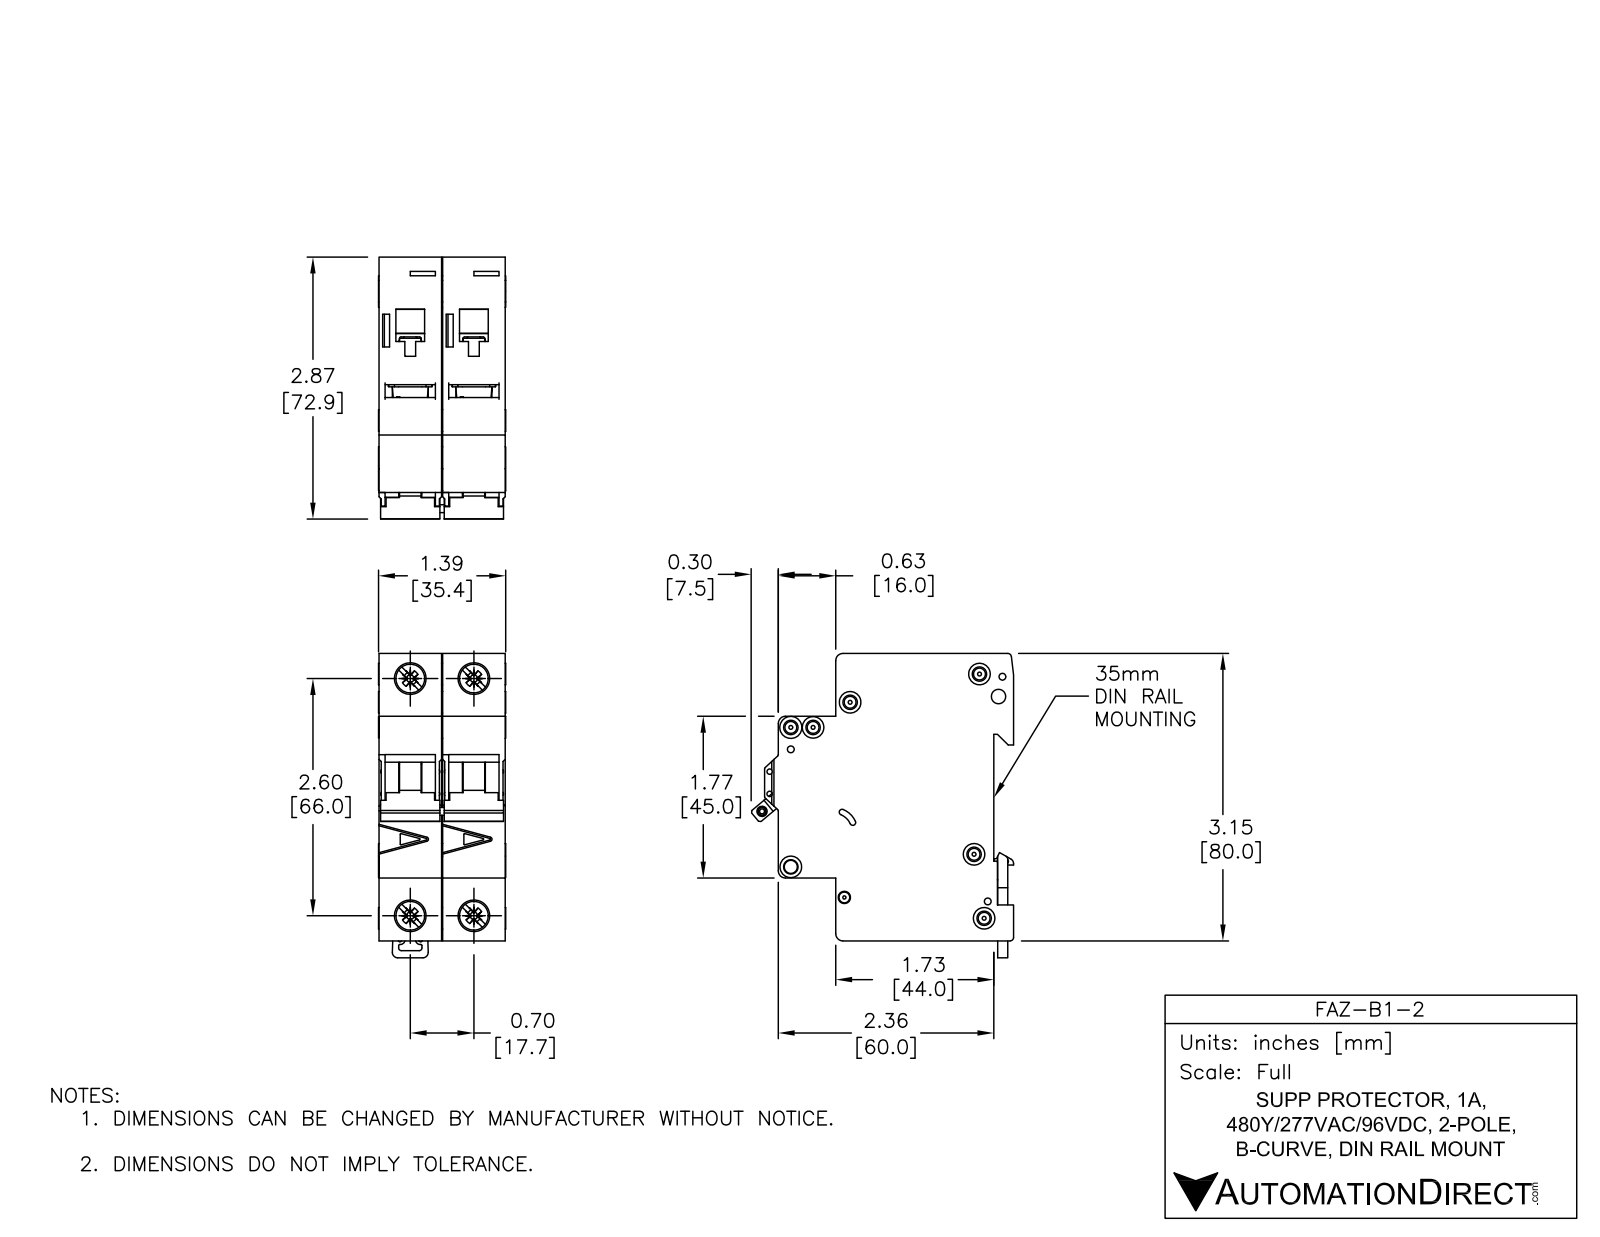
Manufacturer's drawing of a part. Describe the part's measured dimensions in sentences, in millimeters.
The part is named "FAZ-B1-2". Its 3-D file was written by "SolidWorks 2014 (AUTOMOTIVE_DESIGN)". It is 8 solids with 1104 faces: 466 planar, 396 cylindrical and 242 other. Overall it measures 84.78 by 73.04 by 35.4 millimeters. Its volume is 149 808 cubic millimeters and its surface area 38 799 square millimeters. Round holes: 6 of diameter 3.6, 3 of diameter 1.9, 2 of diameter 1.09, 2 of diameter 1.5, 2 of diameter 4, 2 of diameter 7.15, 2 of diameter 8.2, 1 of diameter 2.15, 1 of diameter 2.2, 1 of diameter 2.55, 1 of diameter 3.3, 1 of diameter 3.4. Round bosses or shafts: 4 of diameter 6, 2 of diameter 8.2, 2 of diameter 2.5. Partial cylindrical surfaces (rounded edges, fillets, slot ends): 49 of radius 0.25, 19 of radius 0.5, 10 of radius 2, 8 of radius 0.2, 8 of radius 1, 2 of radius 0.8, 2 of radius 1.8, 2 of radius 3. The main face-to-face distances are 17.7, 17.5, 35.2, 79.48, 5.5, 49.5, 44, 65.5, 60, 16. The hole center spacings are 6.2, 13.64, 17.7, 66, 68.33, 4.81, 5.19, 5.61.
